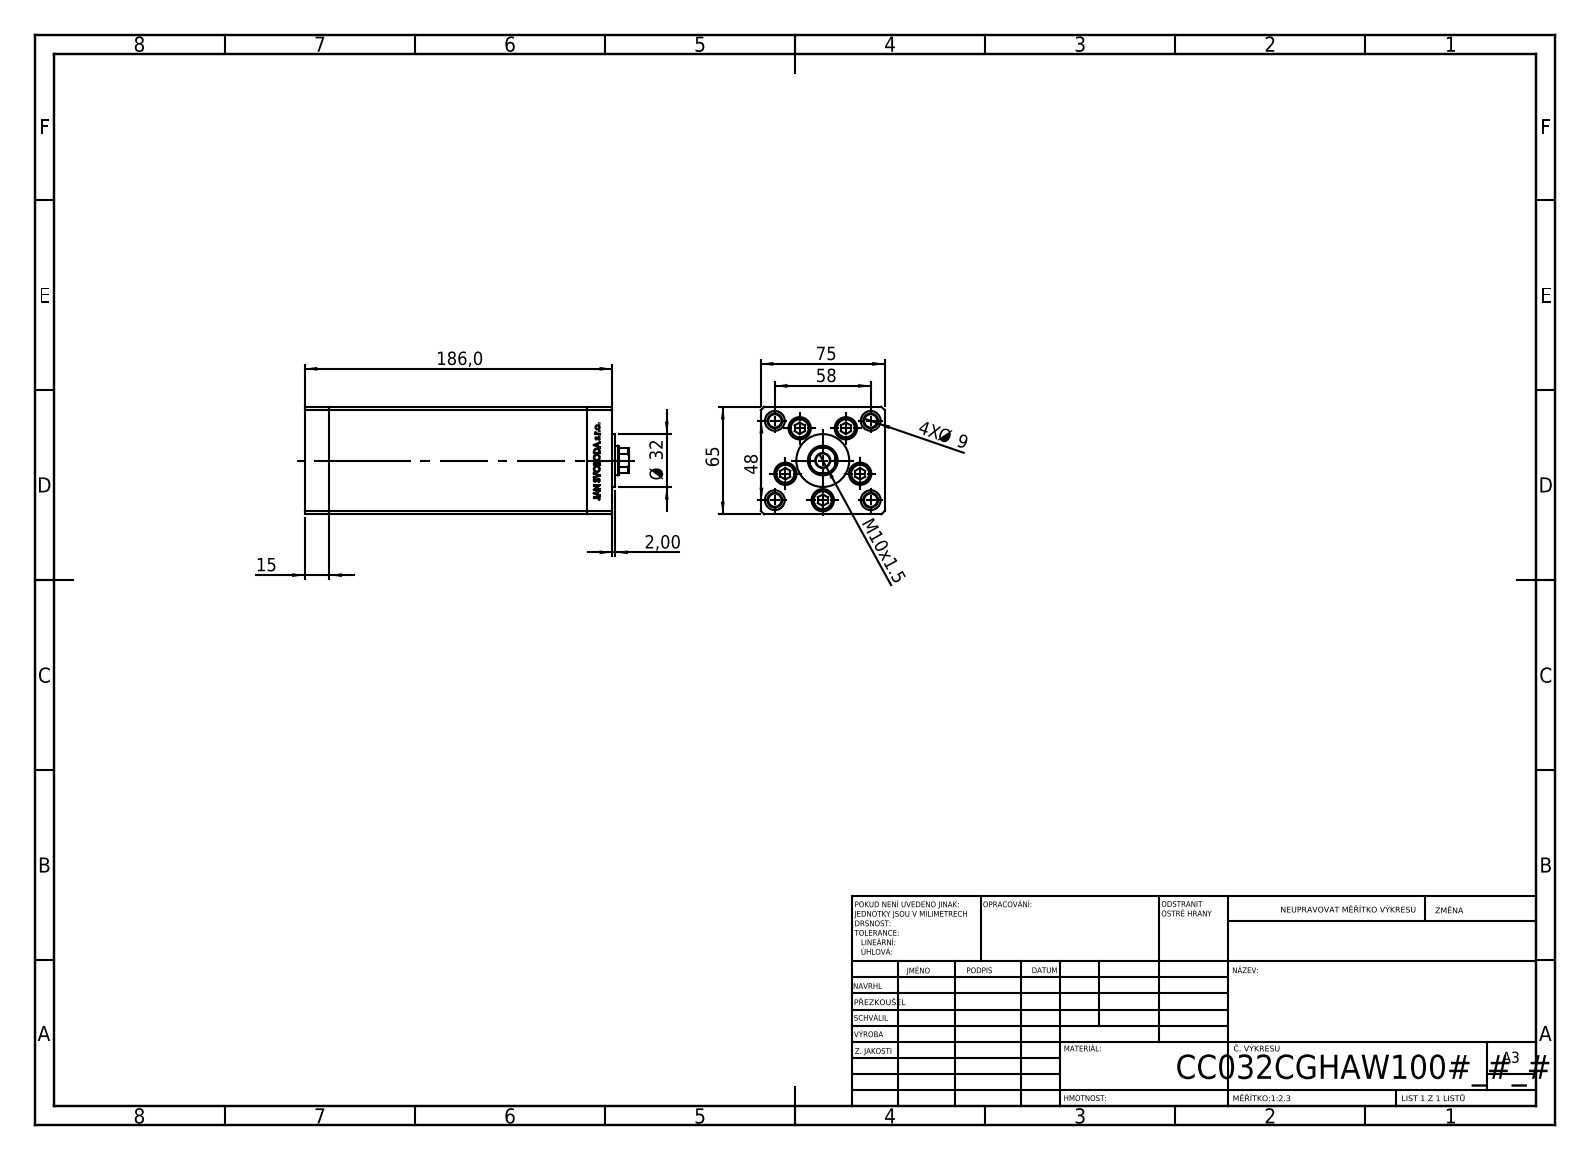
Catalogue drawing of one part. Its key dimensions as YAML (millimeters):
part_name: "V220C FRONT; V220C BACK_C; ALLEN BOLT; V220C_C MIDDLE (+1 more)"
step_written_by: "SolidWorks 2019 (CONFIG_CONTROL_DESIGN)"
units: millimeters
bodies: {solids: 13, faces: 1179, planar: 542, cylindrical: 175, other: 462}
overall_size: [196, 75, 65]
volume: 754279
surface_area: 155117
round_holes:
  - {diameter: 9, count: 9}
  - {diameter: 13.5, count: 5}
  - {diameter: 2, count: 4}
  - {diameter: 8, count: 4}
  - {diameter: 12, count: 4}
  - {diameter: 13.16, count: 4}
  - {diameter: 8.5, count: 1}
  - {diameter: 12.5, count: 1}
  - {diameter: 18, count: 1}
round_bosses_or_shafts:
  - {diameter: 8, count: 5}
  - {diameter: 12.5, count: 4}
  - {diameter: 32, count: 1}
partial_cylinders:
  - {radius: 0.93, count: 2}
  - {radius: 8.5, count: 1}
face_to_face_distances: [75, 65, 15, 156, 171, 186, 28, 13, 54.5, 10.5]
hole_center_spacings: [24, 37.64, 15.67, 17.22, 27.71, 28.83, 29, 32.63]
